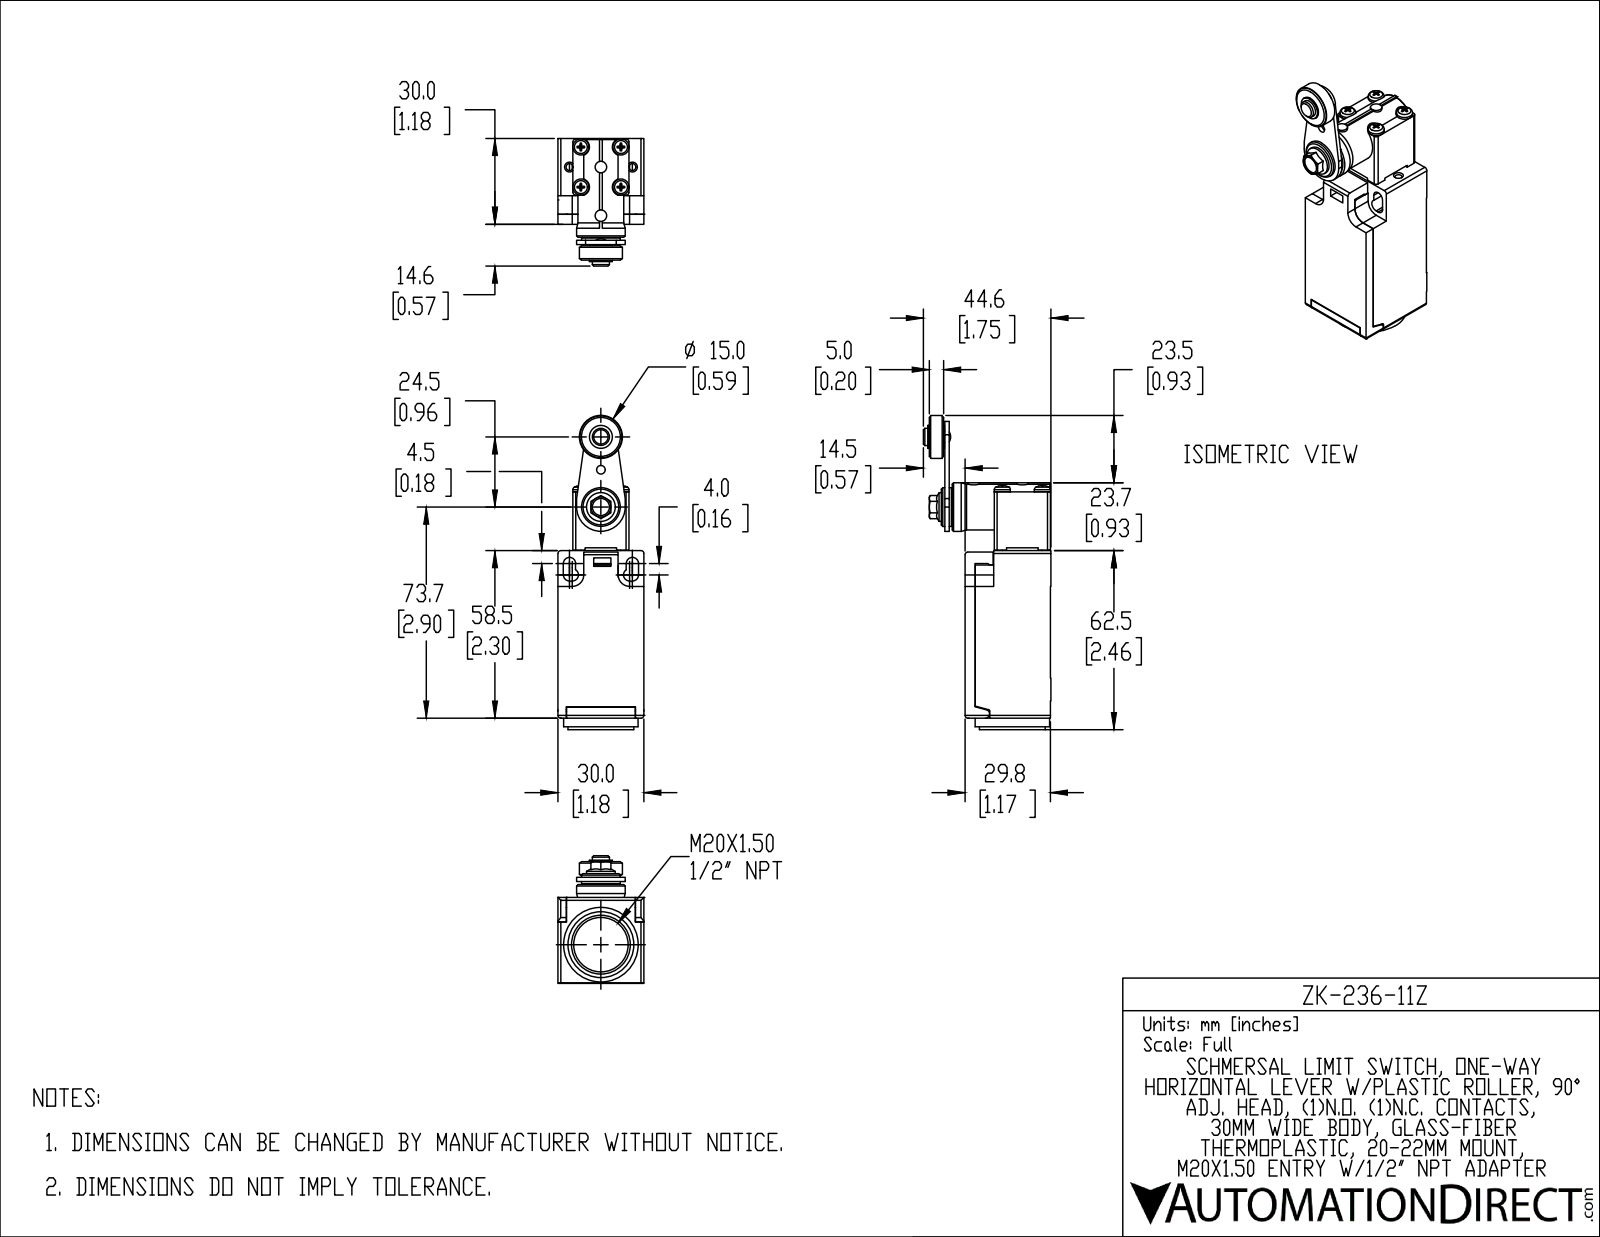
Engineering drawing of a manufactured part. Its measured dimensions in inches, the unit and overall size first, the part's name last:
Units: inches
Overall size (bounding box): 4.319 × 1.754 × 1.181
Round holes (diameter × count): ⌀0.094 ×6, ⌀0.126 ×4, ⌀0.118 ×1, ⌀0.236 ×1, ⌀0.512 ×1, ⌀0.545 ×1, ⌀0.748 ×1
Round bosses / shafts (diameter × count): ⌀0.221 ×4, ⌀0.213 ×4, ⌀0.157 ×3, ⌀1.024 ×1, ⌀0.906 ×1, ⌀0.669 ×1, ⌀0.63 ×1, ⌀0.591 ×1
Partial cylindrical surfaces — rounded edges, fillets, slot ends (radius × count): R0.039 ×10, R0.085 ×6, R0.059 ×5, R0.118 ×4, R0.157 ×2, R0.008 ×1, R0.024 ×1, R0.213 ×1
Main face-to-face distances: 1.181, 1.035, 0.138, 1.173, 0.205, 0.976, 1.043, 0.772, 0.236, 0.157
Hole centre spacings: 0.317, 0.39, 0.551, 0.76, 0.308, 0.433, 0.454, 0.497
Volume: 3.714 in³ · Surface area: 30.13 in²
Bodies: 2 solids, 348 faces (237 planar, 84 cylindrical, 27 other)
Part name (STEP PRODUCT): ZK-236-11Z
STEP written by: SolidWorks 2019 (AUTOMOTIVE_DESIGN)
